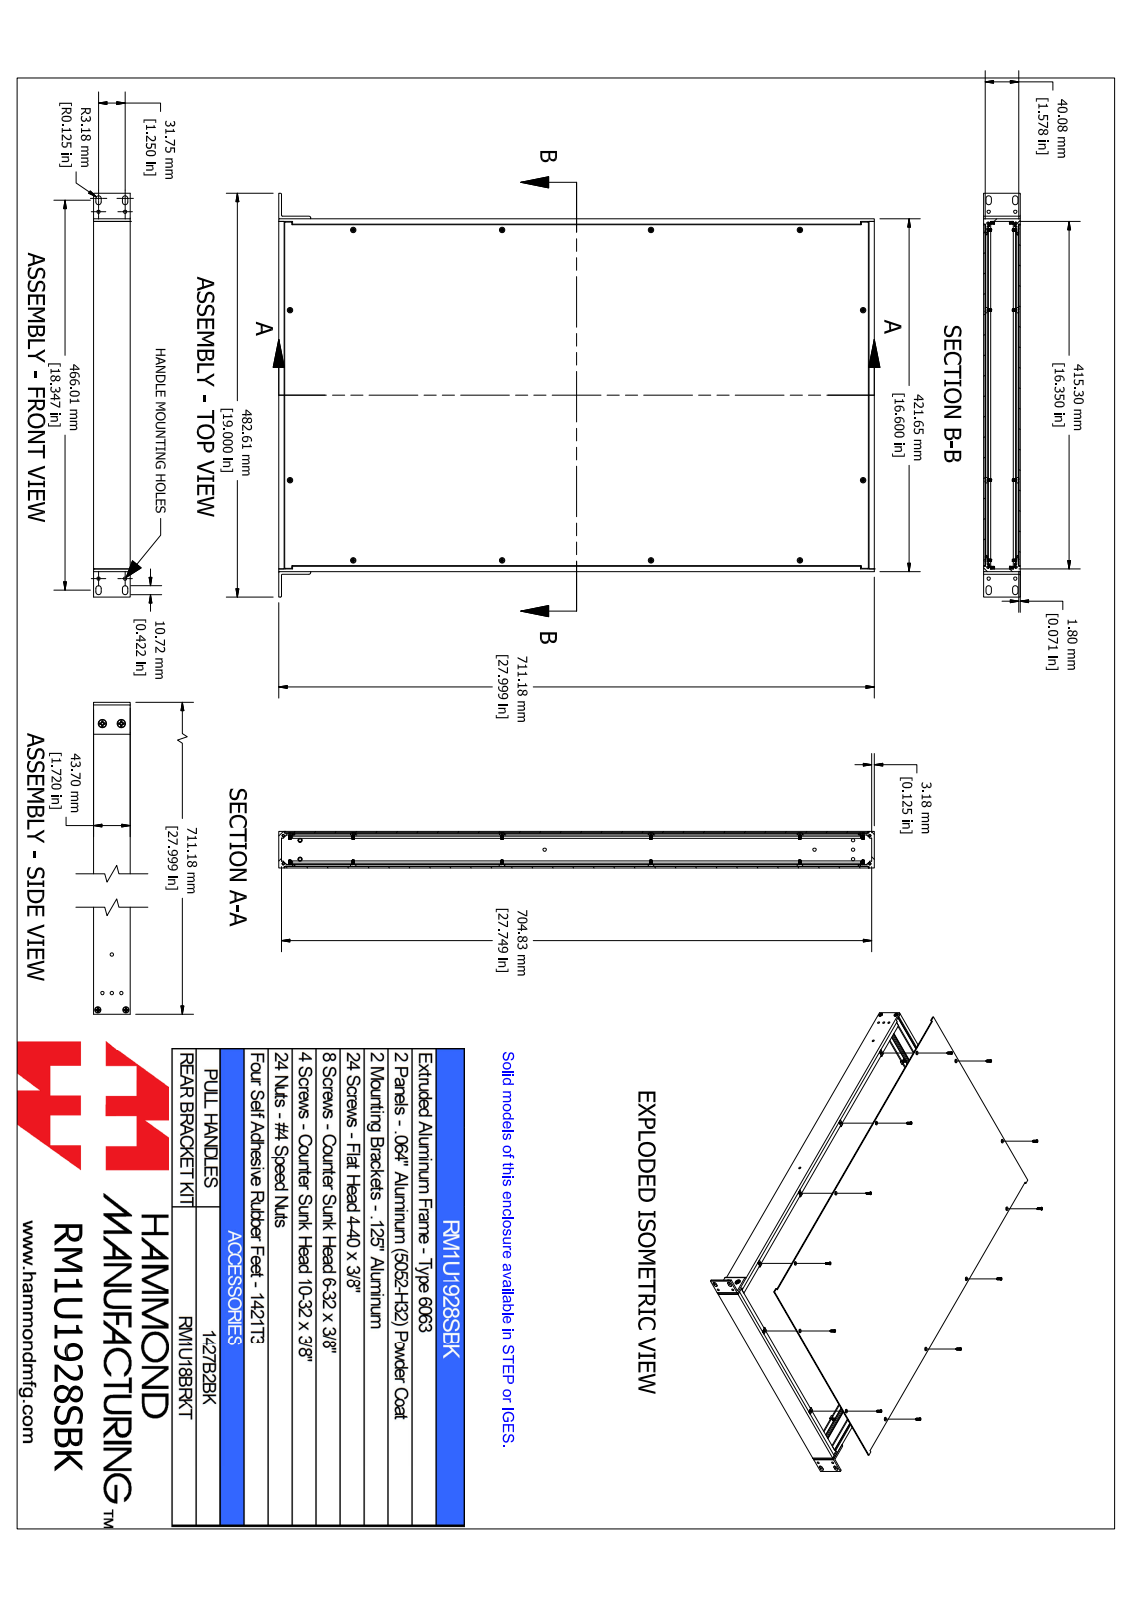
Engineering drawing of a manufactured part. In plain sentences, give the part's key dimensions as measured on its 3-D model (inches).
The part is named "RM1U1928SBK". Its 3-D file was written by "SolidWorks 2021 (AUTOMOTIVE_DESIGN)". It is 68 solids with 2630 faces: 1076 planar, 622 cylindrical and 932 other. Overall it measures 27.999 by 19 by 1.72 inches. Its volume is 94.09 cubic inches and its surface area 2 355 square inches. Round holes: 16 of diameter 0.157, 12 of diameter 0.16, 8 of diameter 0.165, 4 of diameter 0.156, 4 of diameter 0.157, 4 of diameter 0.169, 3 of diameter 0.159, 2 of diameter 0.197. Round bosses or shafts: 12 of diameter 0.2, 12 of diameter 0.112, 4 of diameter 0.238, 4 of diameter 0.138, 2 of diameter 0.36, 2 of diameter 0.19. Partial cylindrical surfaces (rounded edges, fillets, slot ends): 96 of radius 0.01, 96 of radius 0.024, 48 of radius 0.009, 48 of radius 0.014, 16 of radius 0.015, 16 of radius 0.038, 16 of radius 0.039, 10 of radius 0.035. The main face-to-face distances are 0.071, 1.649, 1.72, 1.578, 0.125, 16.476, 0.087, 1.633, 0.016, 1.562. The hole center spacings are 7, 17.049, 14, 20.92, 26.707, 4.803, 8, 10.662.
